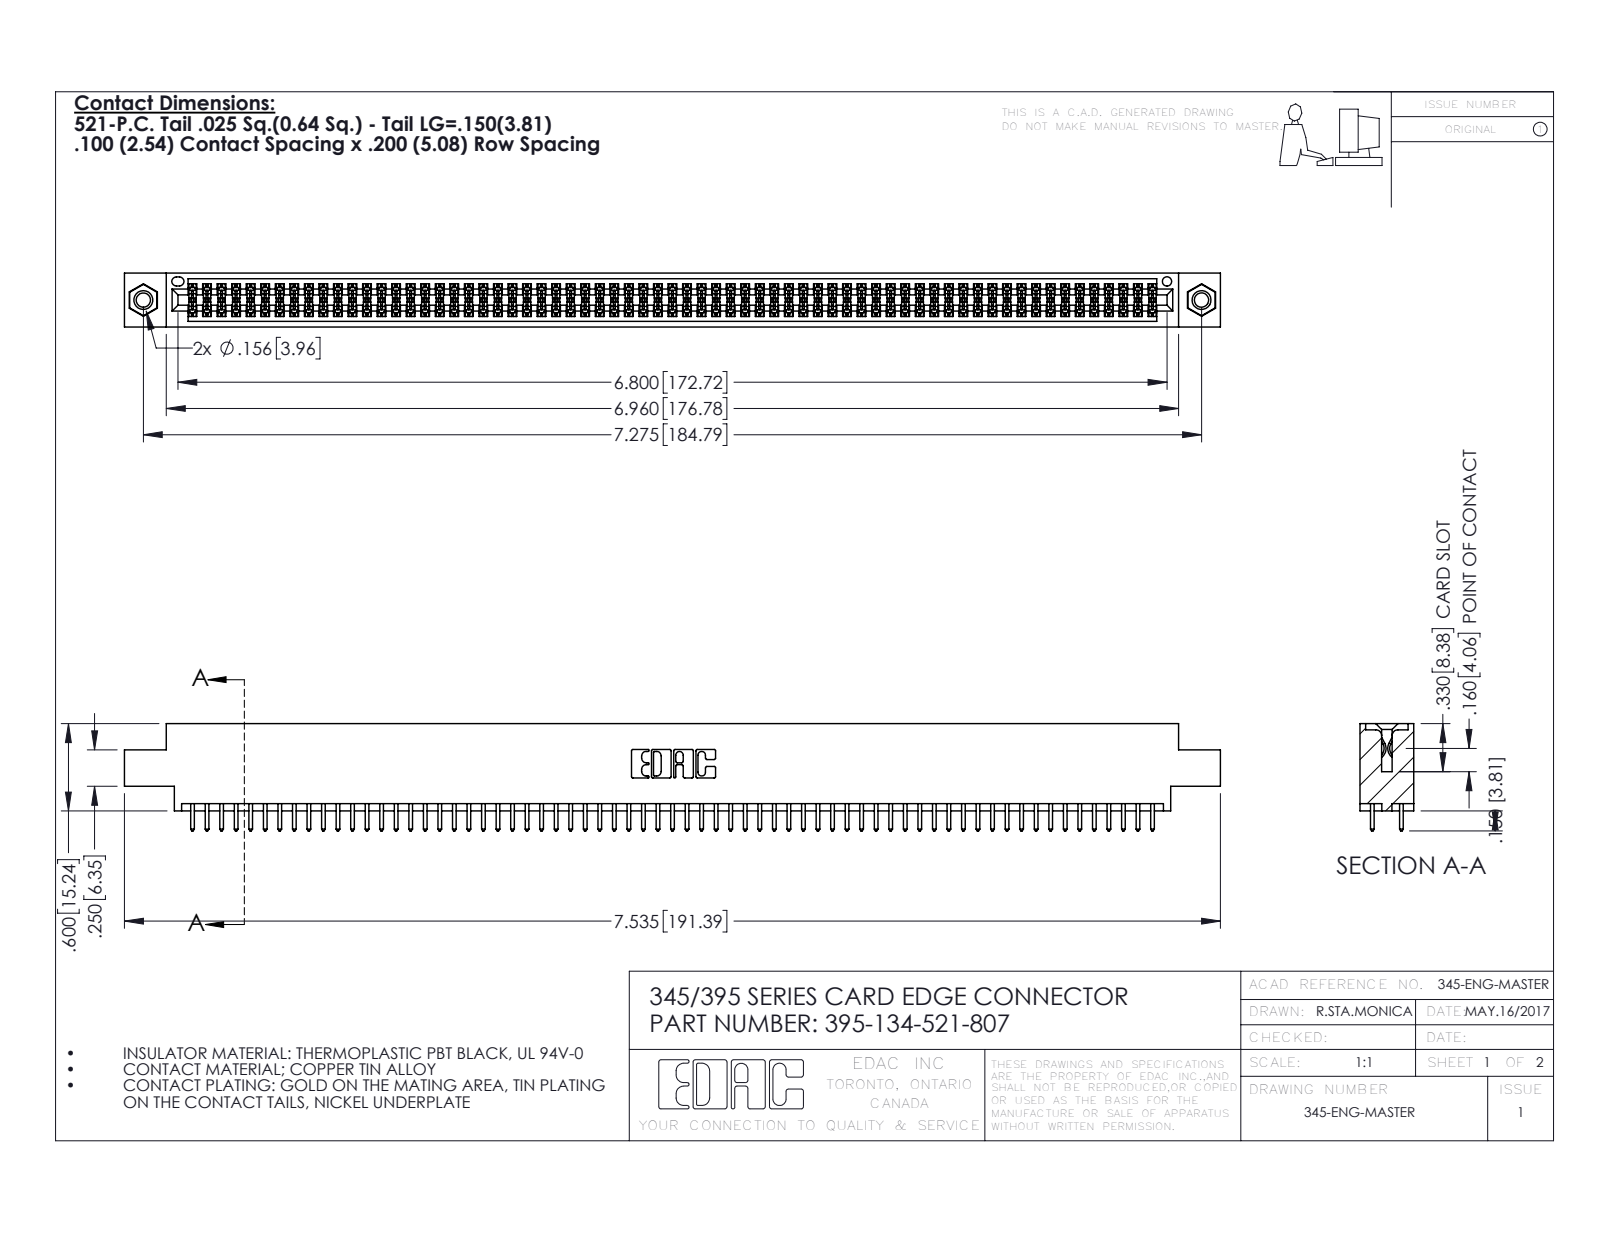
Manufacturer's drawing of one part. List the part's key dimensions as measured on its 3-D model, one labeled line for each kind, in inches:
Part name (STEP PRODUCT): 345-250-001_345-250-005-103; 345-292-001_345-293-121; 395-134-521-807; 345 Part_0.170 Offset - 0.156 Dia-TI
STEP written by: SolidWorks 2016 (CONFIG_CONTROL_DESIGN)
Units: inches
Bodies: 137 solids, 6890 faces (4538 planar, 2336 cylindrical, 16 other)
Overall size (bounding box): 7.535 × 0.737 × 0.37
Volume: 1.138 in³ · Surface area: 43.18 in²
Round holes (diameter × count): ⌀0.098 ×2, ⌀0.125 ×2, ⌀0.156 ×2, ⌀0.064 ×1
Round bosses / shafts (diameter × count): ⌀0.155 ×2
Partial cylindrical surfaces — rounded edges, fillets, slot ends (radius × count): R0.006 ×201, R0.01 ×134, R0.01 ×22, R0.007 ×6, R0.031 ×6, R0.026 ×3, R0.014 ×2, R0.019 ×2
Main face-to-face distances: 0.072, 0.298, 0.2, 0.37, 0.098, 0.272, 0.025, 0.225, 0.175, 0.149
Hole centre spacings: 0.27, 7.039, 7.275
